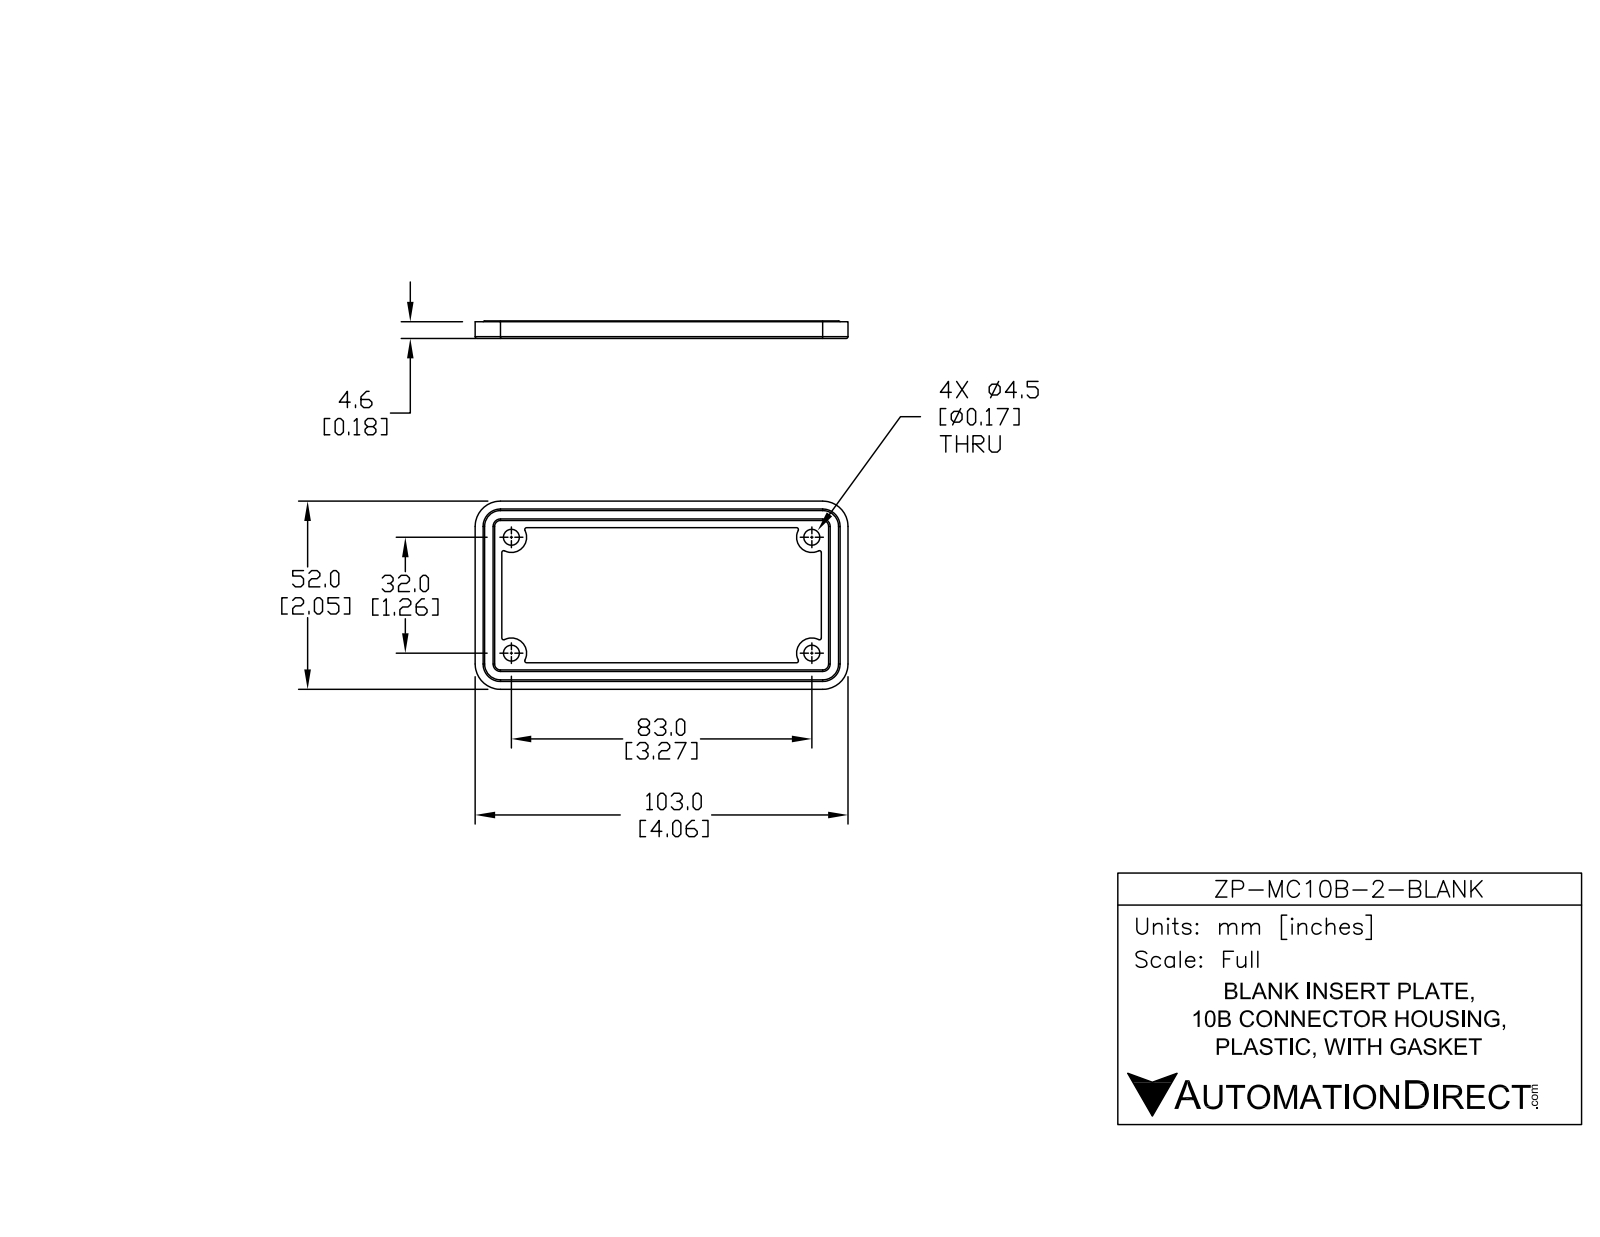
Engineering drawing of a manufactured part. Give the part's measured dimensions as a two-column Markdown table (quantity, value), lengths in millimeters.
| quantity | value |
| --- | --- |
| part name | ZP-MC10B-2-BLANK |
| STEP written by | SolidWorks 2014 (AUTOMOTIVE_DESIGN) |
| units | millimeters |
| bodies | 1 solid, 65 faces (13 planar, 40 cylindrical, 12 other) |
| overall size | 103 × 52 × 4.85 |
| volume | 14 977 mm³ |
| surface area | 12 858 mm² |
| round holes (diameter × count) | 4.4 × 4 |
| partial cylindrical surfaces (radius × count) | 0.5 × 20, 4.2 × 4, 7 × 4 |
| main face-to-face distances | 1.6, 3, 4.6, 3.25, 4.85, 7.36, 44.64, 52, 37.28, 103 |
| hole center spacings | 32, 83, 88.96 |
